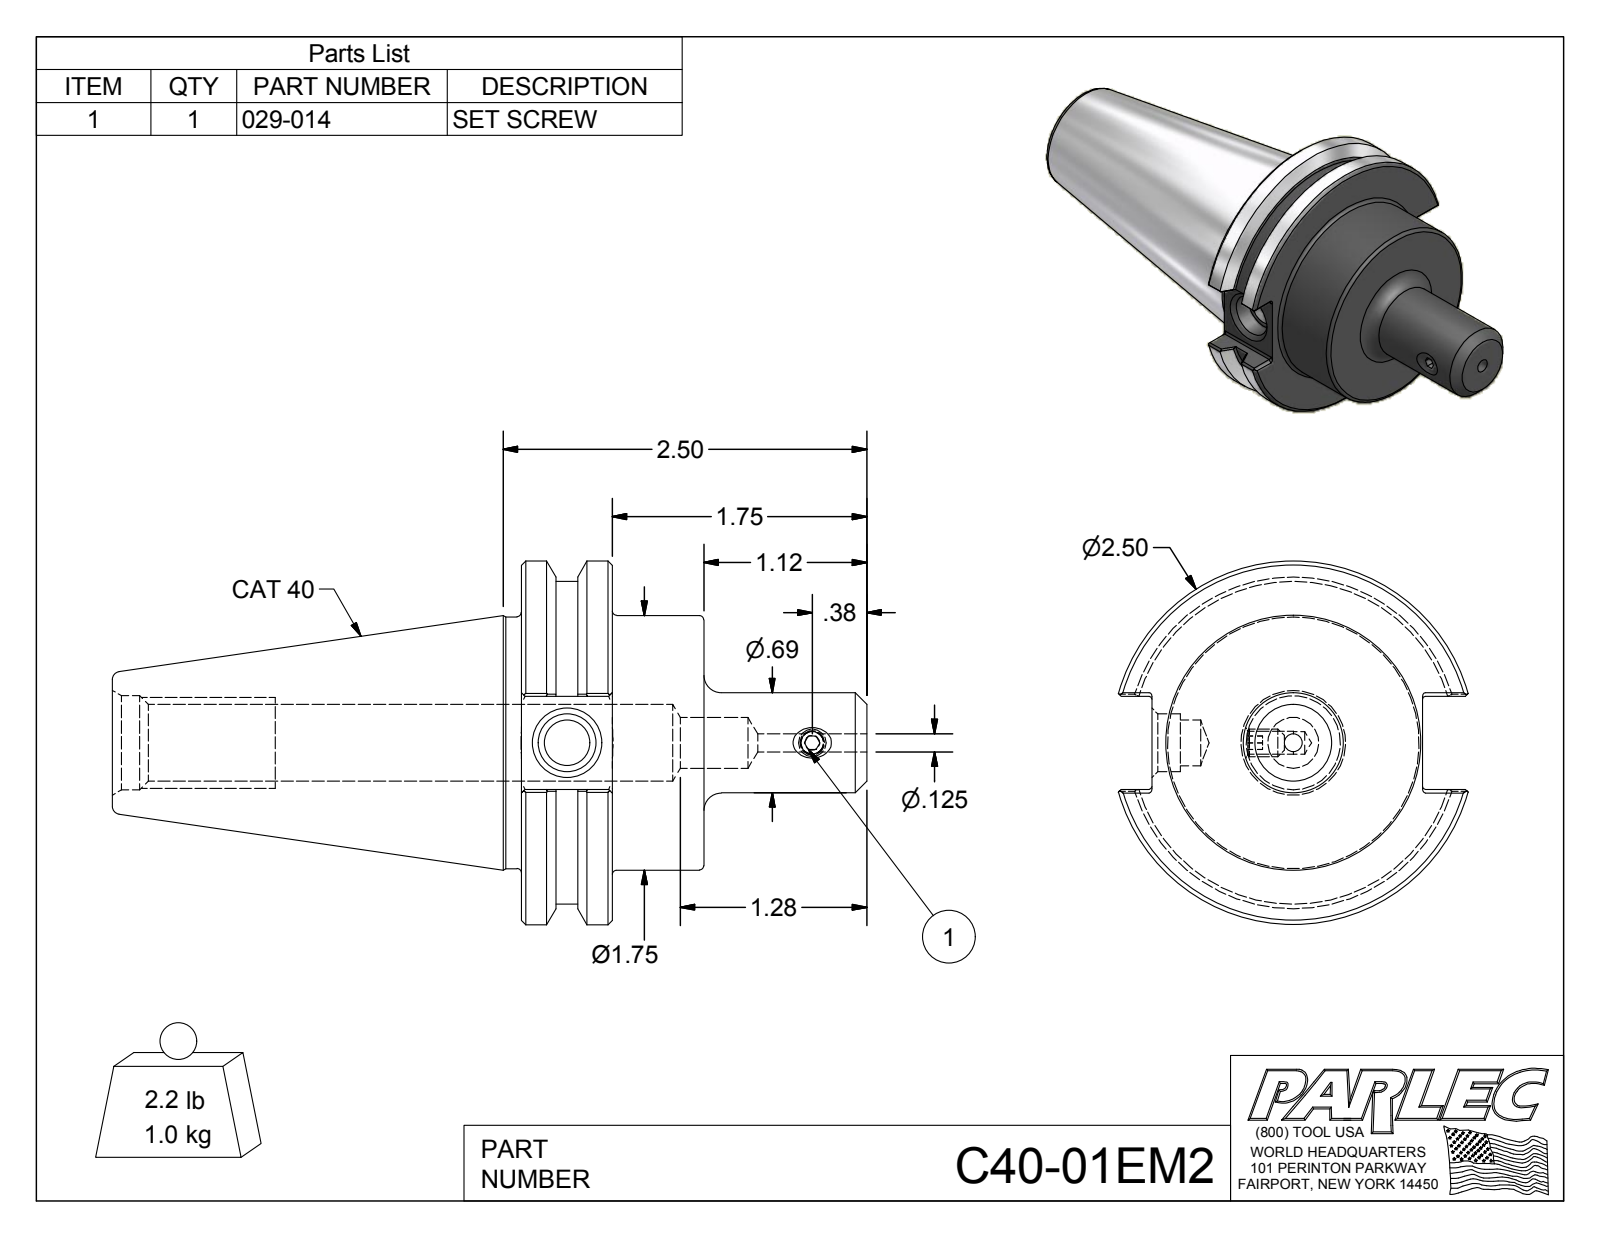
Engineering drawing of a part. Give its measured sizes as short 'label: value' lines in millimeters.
name: C40-01EM2; C40-01EM2-1; 029-014
written by: Autodesk Inventor 2012 (AUTOMOTIVE_DESIGN)
unit: mm
bodies: 2 solids, 108 faces (41 planar, 31 cylindrical, 36 other)
size: 131.7 × 63.5 × 61.1
volume: 129 400 mm³; area: 25 210 mm²
holes: 1× ⌀3.2, 1× ⌀3.9, 1× ⌀4, 1× ⌀8, 1× ⌀8.9, 1× ⌀10.1, 1× ⌀13.4, 1× ⌀16.5
bosses: 1× ⌀63.5, 1× ⌀56.4, 1× ⌀44.5, 1× ⌀43.9, 1× ⌀17.4, 1× ⌀4.8
rounds: 12× R0.5
face distances: 15.9, 31.9, 16, 16.3, 60.3, 44.5, 28.4, 47.2, 71.4, 87.3
hole spacings: 42.8
